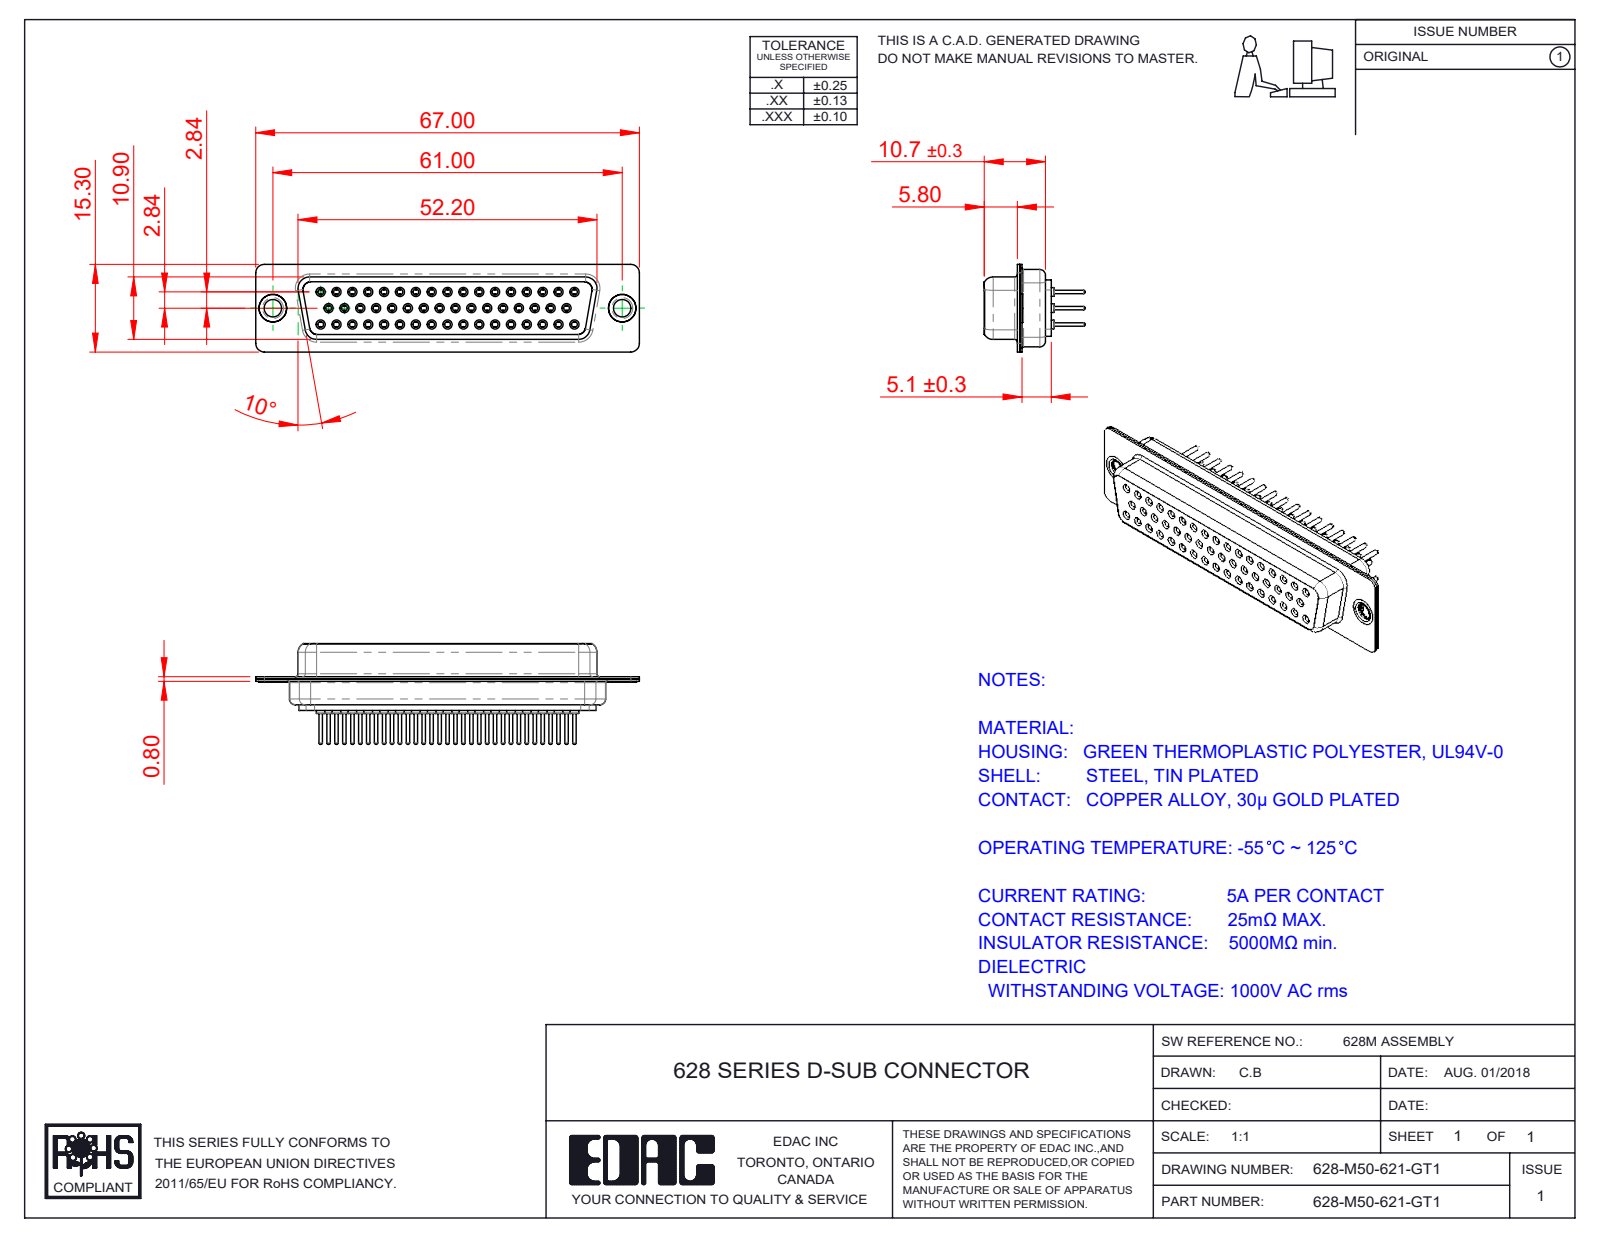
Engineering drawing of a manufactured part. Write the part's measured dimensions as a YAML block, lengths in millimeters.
part_name: "628M Contact Row 3_21; 628M Contact Row 2_21; 628-M50-621-GT1; 628M Shell Rear_50 Contacts (+4 more)"
step_written_by: "SolidWorks 2020 (CONFIG_CONTROL_DESIGN)"
units: millimeters
bodies: {solids: 55, faces: 3003, planar: 817, cylindrical: 1071, other: 1115}
overall_size: [67, 17.6, 15.3]
volume: 6544
surface_area: 14893
round_holes:
  - {diameter: 1, count: 50}
  - {diameter: 1.1, count: 50}
  - {diameter: 1.7, count: 50}
  - {diameter: 1.8, count: 50}
  - {diameter: 2, count: 50}
  - {diameter: 3.05, count: 2}
  - {diameter: 4, count: 2}
  - {diameter: 4.8, count: 2}
round_bosses_or_shafts:
  - {diameter: 2.2, count: 50}
  - {diameter: 1.6, count: 50}
  - {diameter: 1.5, count: 50}
  - {diameter: 0.6, count: 50}
  - {diameter: 5, count: 2}
  - {diameter: 4.9, count: 2}
  - {diameter: 3.55, count: 2}
partial_cylinders:
  - {radius: 1.5, count: 16}
  - {radius: 2, count: 12}
  - {radius: 1.35, count: 8}
  - {radius: 1.6, count: 8}
  - {radius: 0.25, count: 4}
  - {radius: 0.5, count: 4}
  - {radius: 0.6, count: 4}
  - {radius: 0.65, count: 4}
face_to_face_distances: [0.4, 1.3, 11.8, 0.9, 5.5, 5.9, 0.85, 13.1, 5.8, 10.05]
hole_center_spacings: [3.16, 2.77, 5.54, 8.31, 11.08, 13.85, 16.62, 19.39]
